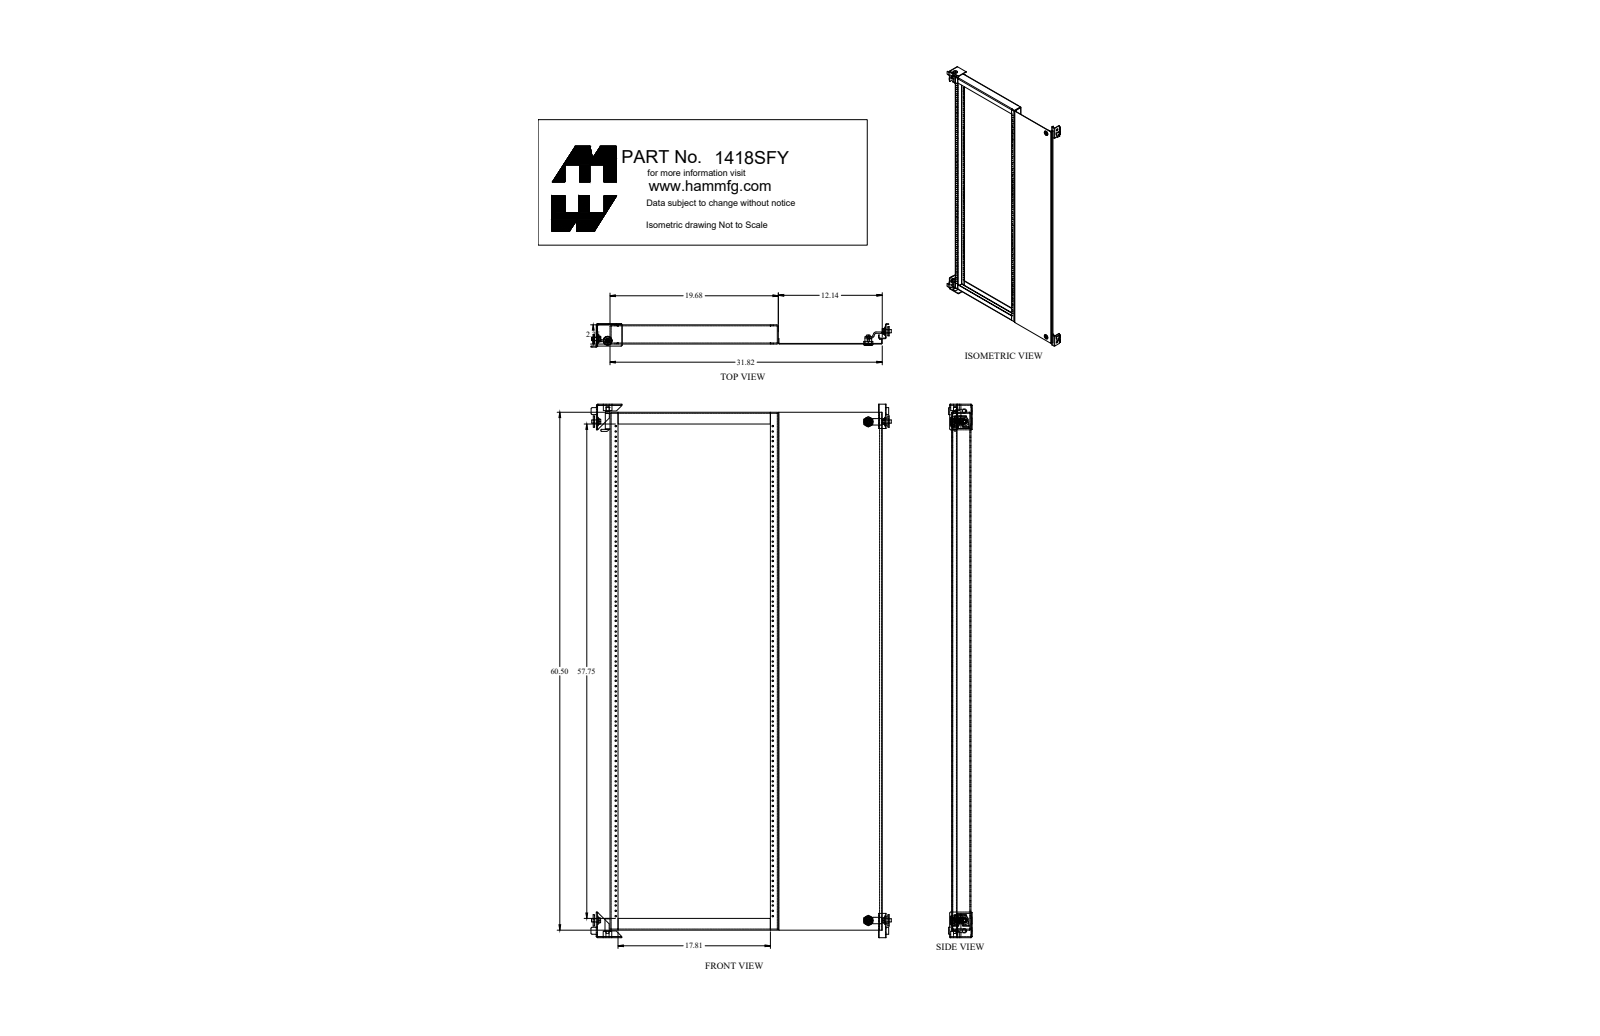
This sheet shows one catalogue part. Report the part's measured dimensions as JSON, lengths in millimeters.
{"part_name": "1418SFY_Default", "step_written_by": "SolidWorks 2019 (CONFIG_CONTROL_DESIGN)", "units": "millimeters", "bodies": {"solids": 38, "faces": 1512, "planar": 474, "cylindrical": 1006, "other": 32}, "overall_size": [1580.5, 894.2, 74.1], "volume_mm3": 2389000, "surface_area_mm2": 2009000, "round_holes": [[4.5, 198], [8, 4], [9.7, 4], [12.7, 4], [11.3, 3], [5.9, 2], [15.9, 2], [19.9, 2], [9.4, 1], [10.4, 1], [11.3, 1], [25.9, 1]], "round_bosses_or_shafts": [[25.4, 5], [17.1, 4], [9.5, 3], [27.9, 2], [13.3, 2], [9, 2], [22.2, 1], [15, 1]], "partial_cylinders_radius": [[1.5, 12], [4.7, 12], [3.2, 11], [5.6, 8], [0.8, 6], [0.9, 6], [2.7, 6], [3.8, 2]], "face_to_face_distances": [1.8, 3.2, 3.2, 54, 496.6, 52.1, 1.3, 50.8, 493.5, 499.8], "hole_center_spacings": [44.5, 133.4, 88.9, 15.9, 28.6, 177.8, 222.3, 15.9]}
